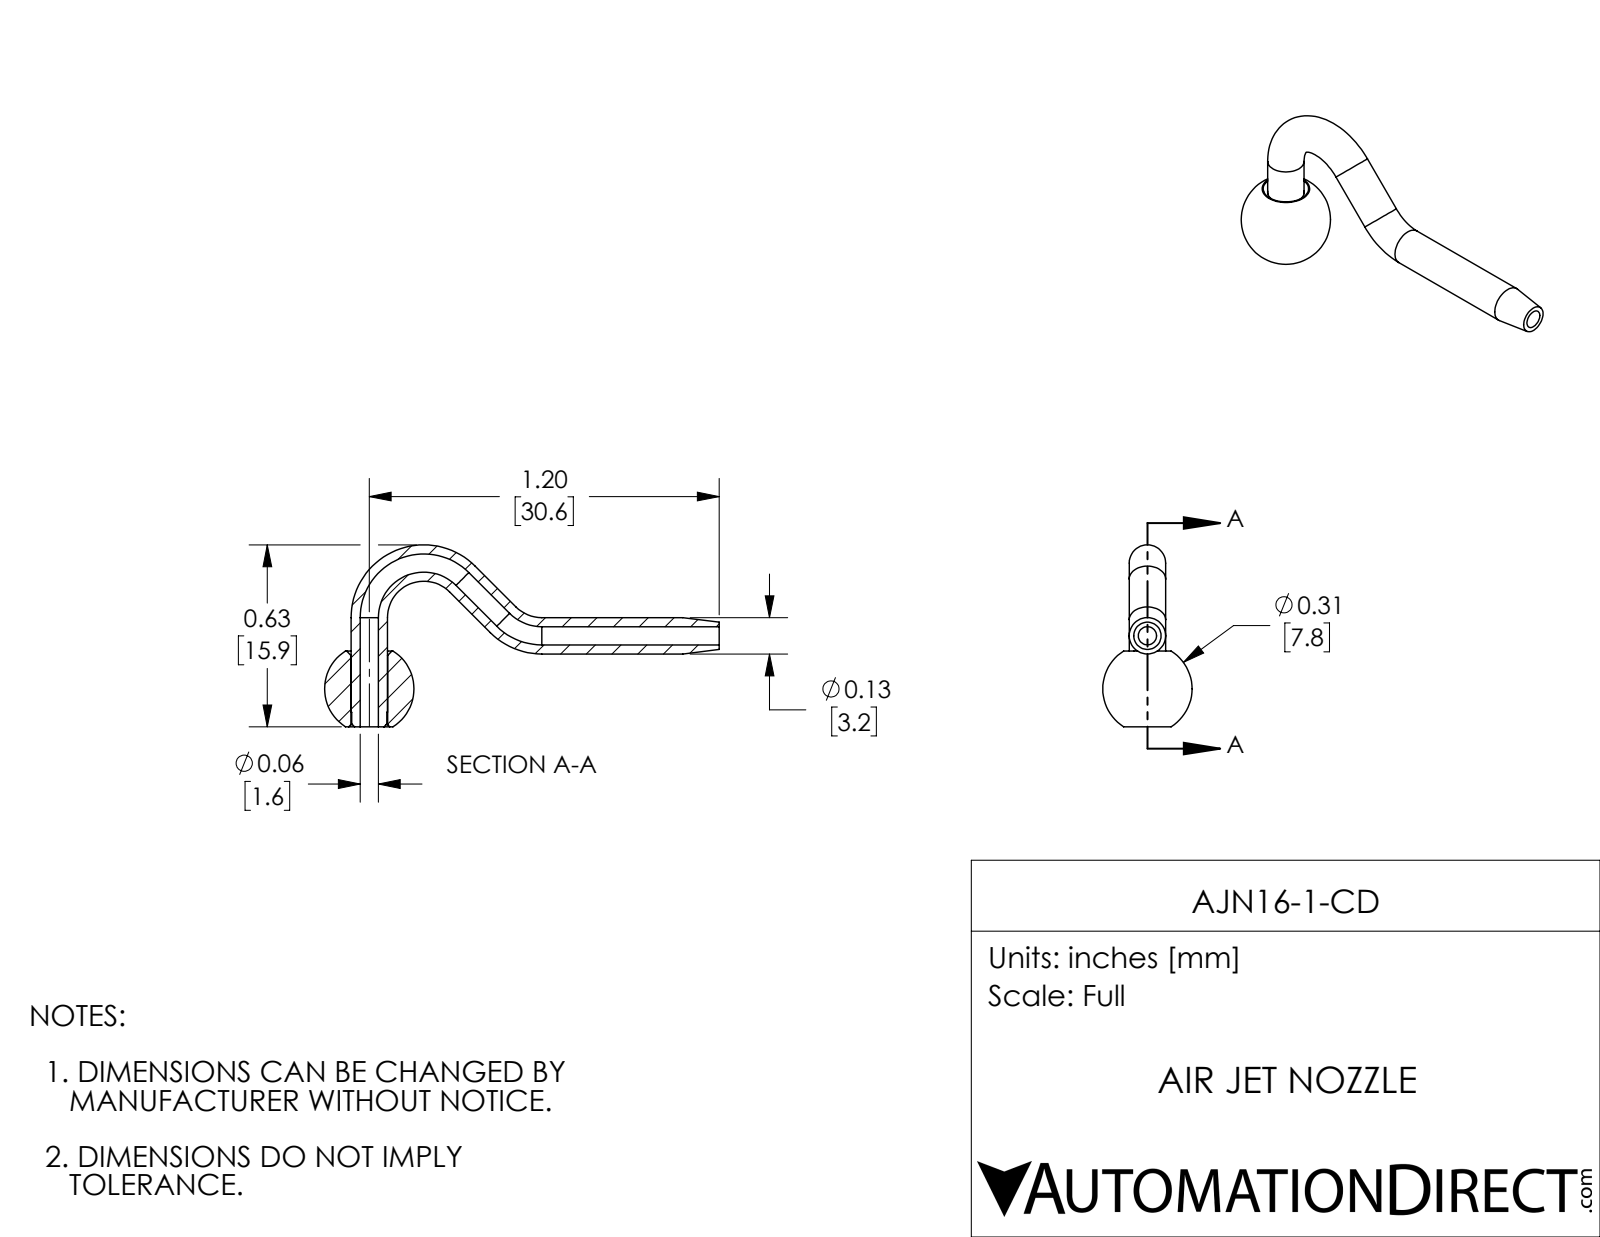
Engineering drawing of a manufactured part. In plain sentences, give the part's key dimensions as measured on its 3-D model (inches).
The part is named "AJN16-1-CD". Its 3-D file was written by "SolidWorks 2018 (AUTOMOTIVE_DESIGN)". It is 2 solids with 39 faces: 5 planar, 16 cylindrical and 18 other. Overall it measures 1.357 by 0.625 by 0.307 inches. Its volume is 0.027 cubic inches and its surface area 1.414 square inches. Round holes: 3 of diameter 0.063, 1 of diameter 0.126. Round bosses or shafts: 2 of diameter 0.125, 1 of diameter 0.125, 1 of diameter 0.121. The main face-to-face distances are 0.26, 0.05, 0.21.
